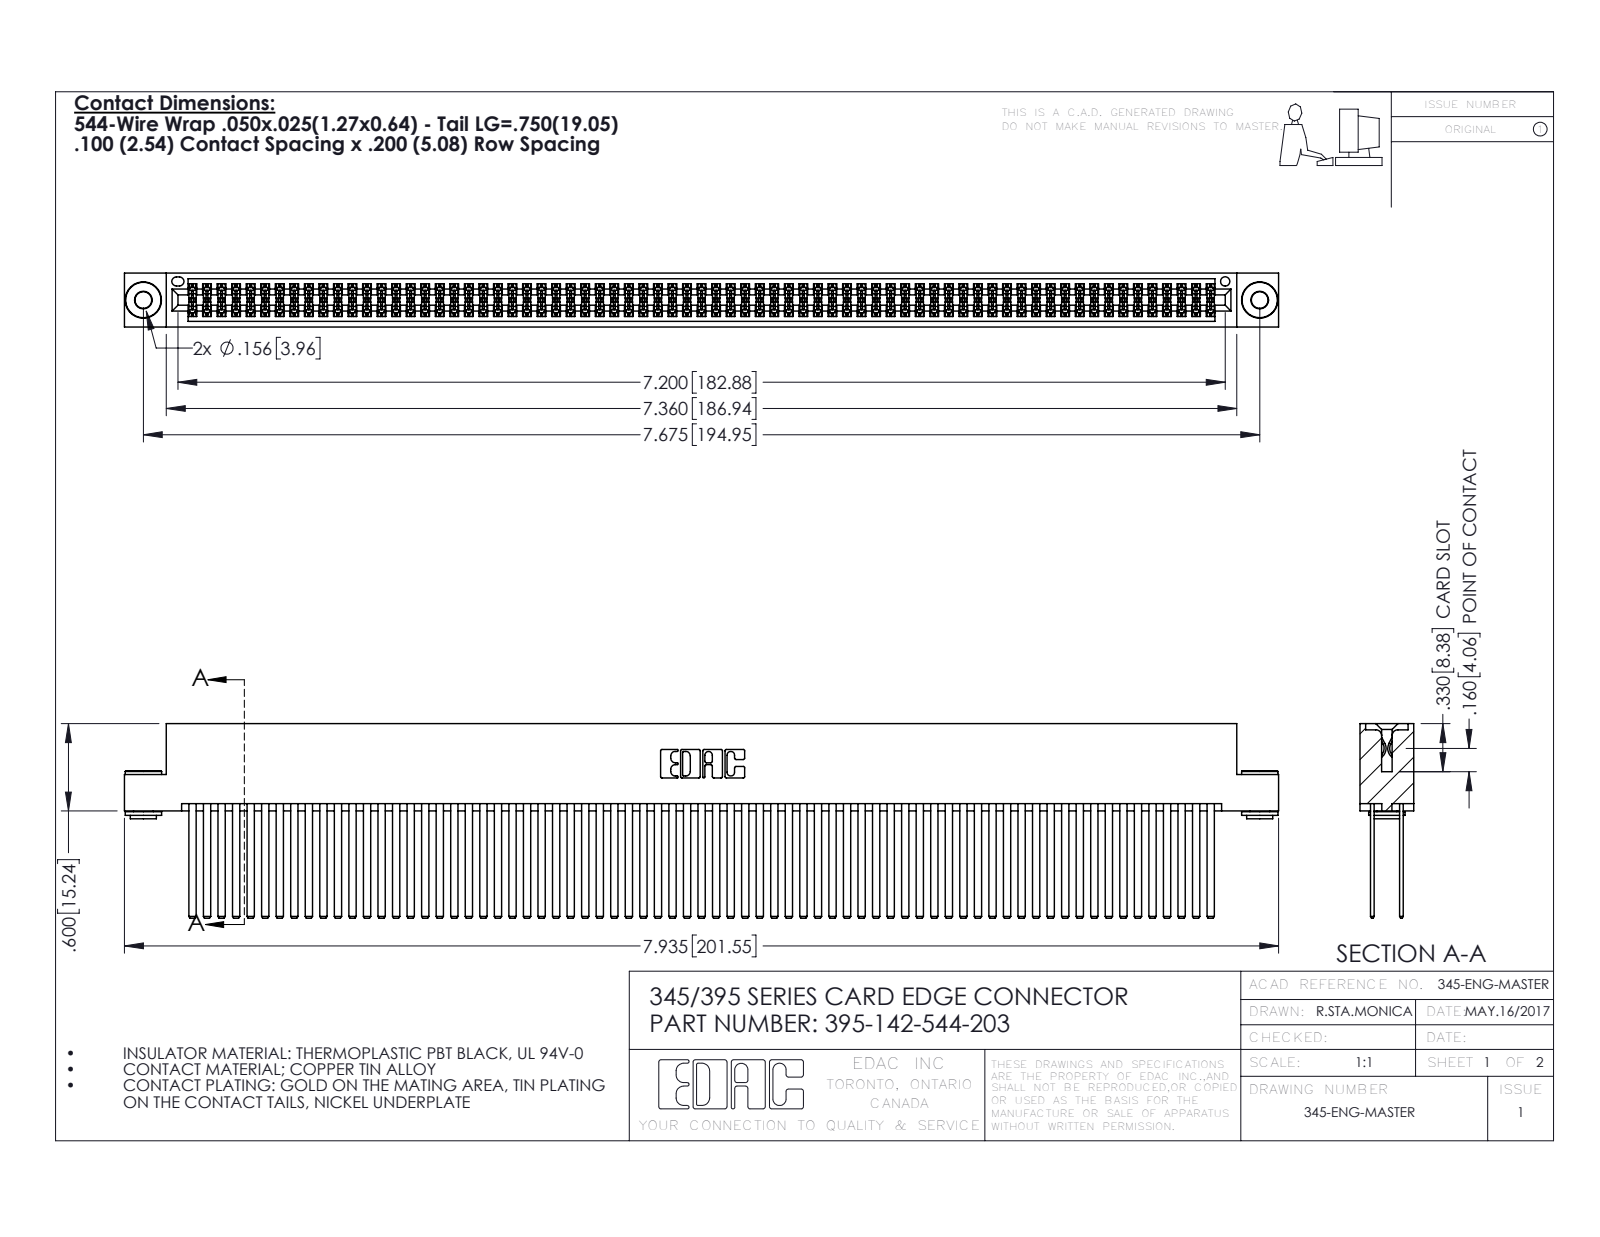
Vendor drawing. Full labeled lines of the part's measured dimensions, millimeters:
Part name (STEP PRODUCT): 345 Part_Flush Mounting Lugs - 0.156 Dia-TH; 345-250-002_345-250-002-102; 345-292-001_345-293-144; 395-142-544-203
STEP written by: SolidWorks 2016 (CONFIG_CONTROL_DESIGN)
Units: millimetres
Bodies: 145 solids, 6412 faces (4208 planar, 2196 cylindrical, 8 other)
Overall size (bounding box): 201.5 × 34 × 9.4
Volume: 21 860 mm³ · Surface area: 38 910 mm²
Round holes (diameter × count): ⌀2.9 ×2, ⌀4 ×2, ⌀1.6 ×1
Round bosses / shafts (diameter × count): ⌀6.4 ×2, ⌀4.6 ×2, ⌀3.5 ×2
Partial cylindrical surfaces — rounded edges, fillets, slot ends (radius × count): R0.2 ×213, R0.3 ×22, R0.2 ×6, R0.8 ×6, R0.7 ×3, R0.4 ×2, R0.5 ×2, R0.6 ×2
Main face-to-face distances: 5.1, 0.6, 1.8, 2.5, 6.9, 7.6, 5.7, 4.4, 9.4, 1.3
Hole centre spacings: 6.9, 189, 194.9
